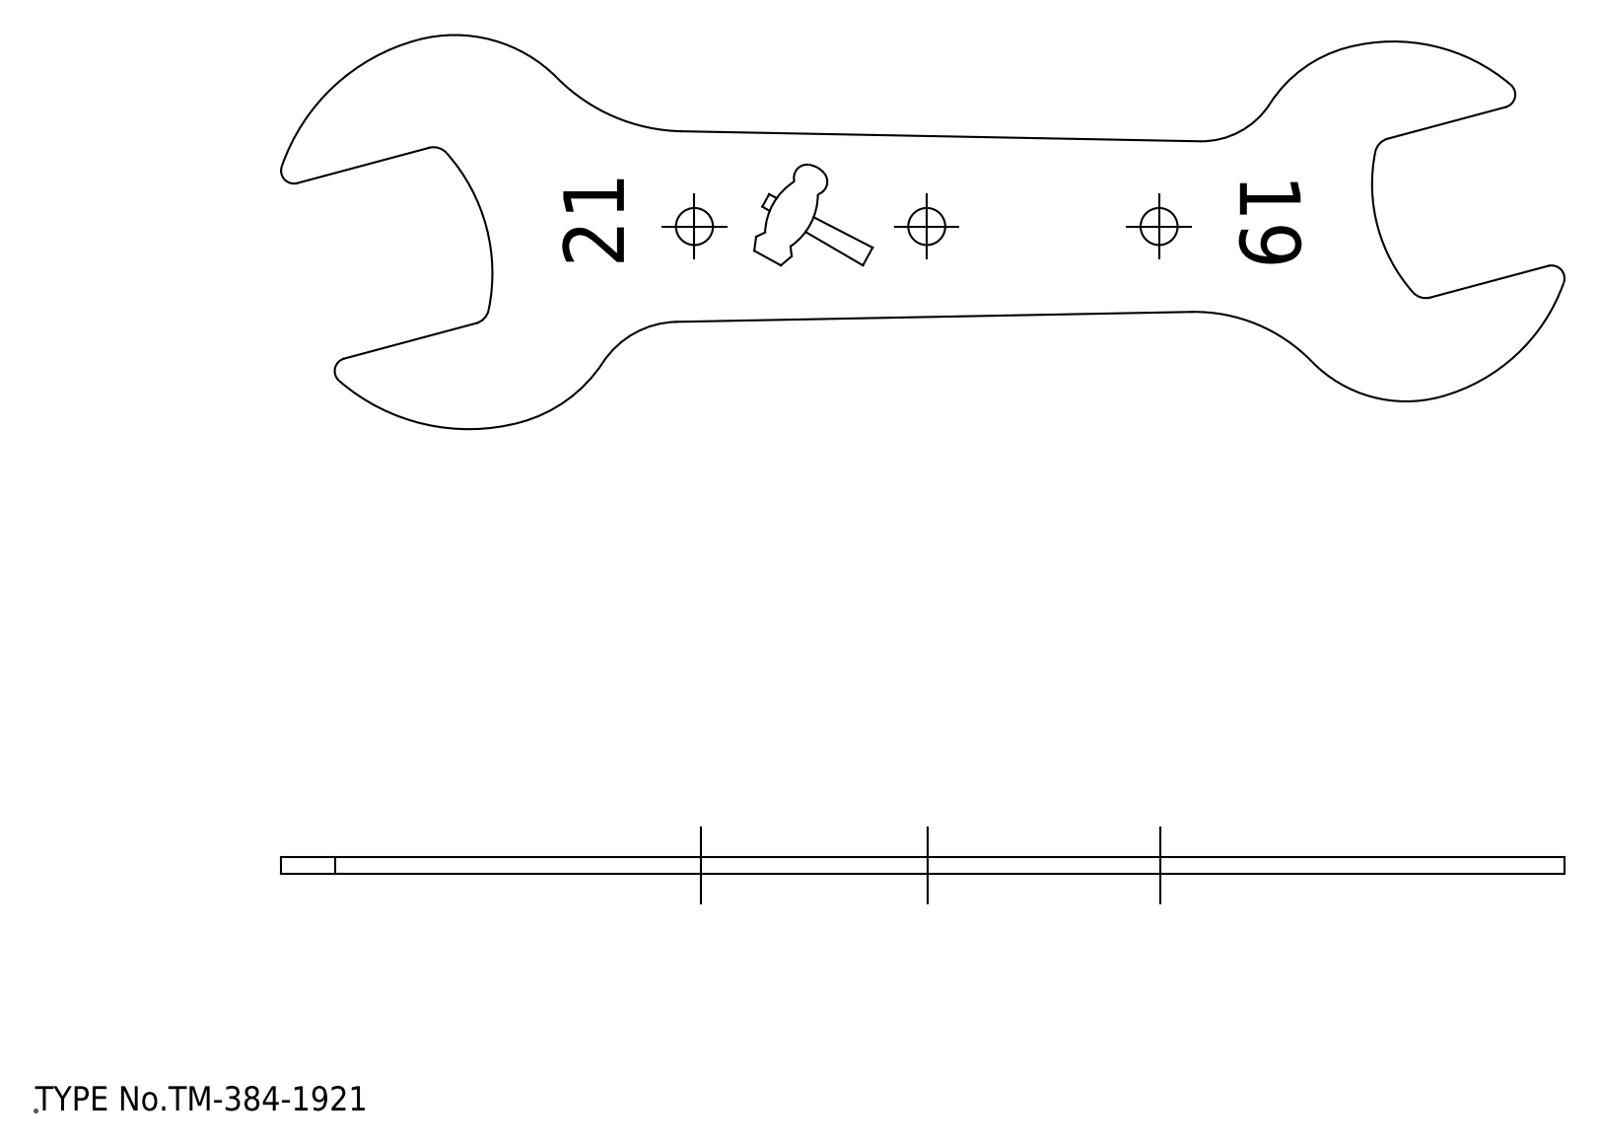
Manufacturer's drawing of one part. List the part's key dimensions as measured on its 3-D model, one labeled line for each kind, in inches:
STEP written by: spGate 19.8.4 (****-****-****-****) (AUTOMOTIVE_DESIGN)
Units: inches
Bodies: 1 solid, 36 faces (8 planar, 28 cylindrical, 0 other)
Overall size (bounding box): 5.872 × 1.802 × 0.079
Volume: 0.413 in³ · Surface area: 11.96 in²
Round holes (diameter × count): ⌀0.169 ×3
Partial cylindrical surfaces — rounded edges, fillets, slot ends (radius × count): R0.059 ×4, R0.079 ×4, R0.827 ×3, R0.602 ×2, R0.657 ×2, R0.748 ×2, R0.374 ×1, R0.413 ×1
Main face-to-face distances: 0.079, 0.831, 1.096, 0.265, 1.848, 1.017, 0.752
Hole centre spacings: 1.063, 2.126
